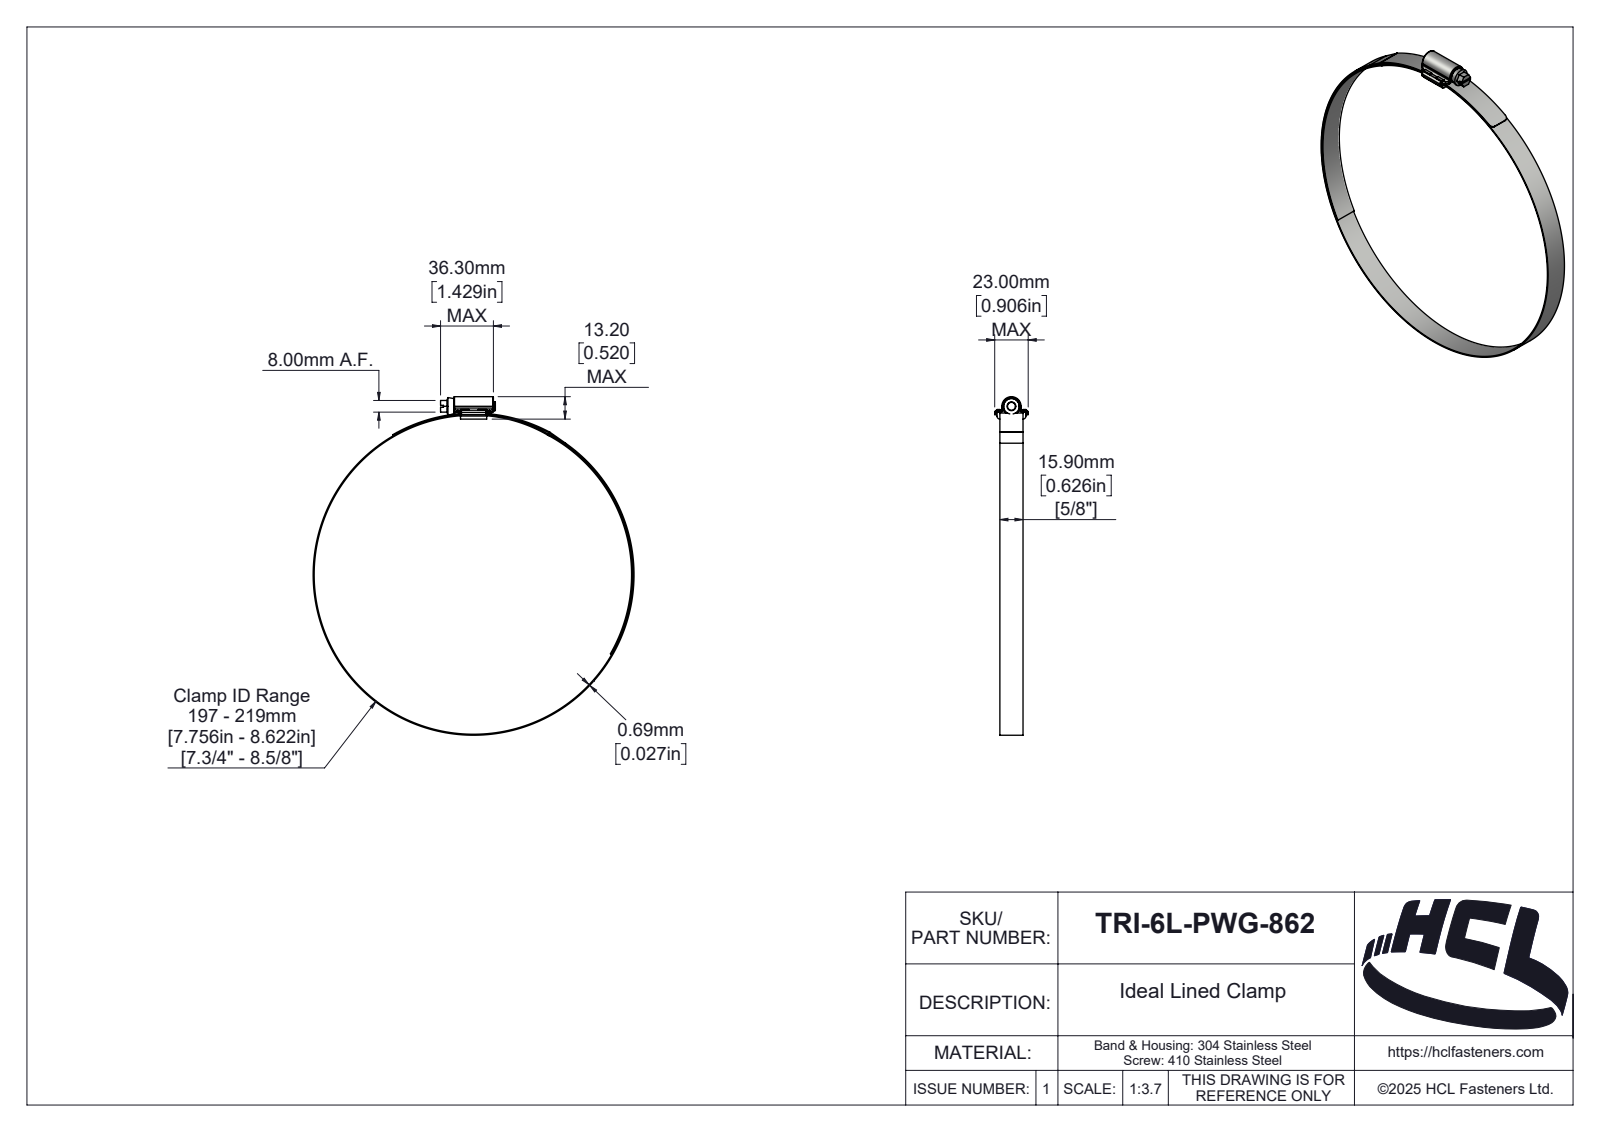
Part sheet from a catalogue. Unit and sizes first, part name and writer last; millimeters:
Units: millimetres
Overall size (bounding box): 232.39 × 220.38 × 23
Round holes (diameter × count): ⌀219 ×1
Round bosses / shafts (diameter × count): ⌀220.38 ×1, ⌀10.7 ×1, ⌀6 ×1
Partial cylindrical surfaces — rounded edges, fillets, slot ends (radius × count): R1 ×14, R0.5 ×4, R1.5 ×4, R2 ×3, R0.1 ×2, R2.1 ×2, R3 ×2, R0.46 ×1
Main face-to-face distances: 15.9, 2, 0.69, 17.9, 4.9, 1.2, 4.55, 3.35, 15.35, 2.55
Volume: 15 909 mm³ · Surface area: 37 013 mm²
Bodies: 4 solids, 268 faces (87 planar, 102 cylindrical, 79 other)
Part name (STEP PRODUCT): TRI-6L-PWG-862
STEP written by: SolidWorks 2025 (AUTOMOTIVE_DESIGN)
